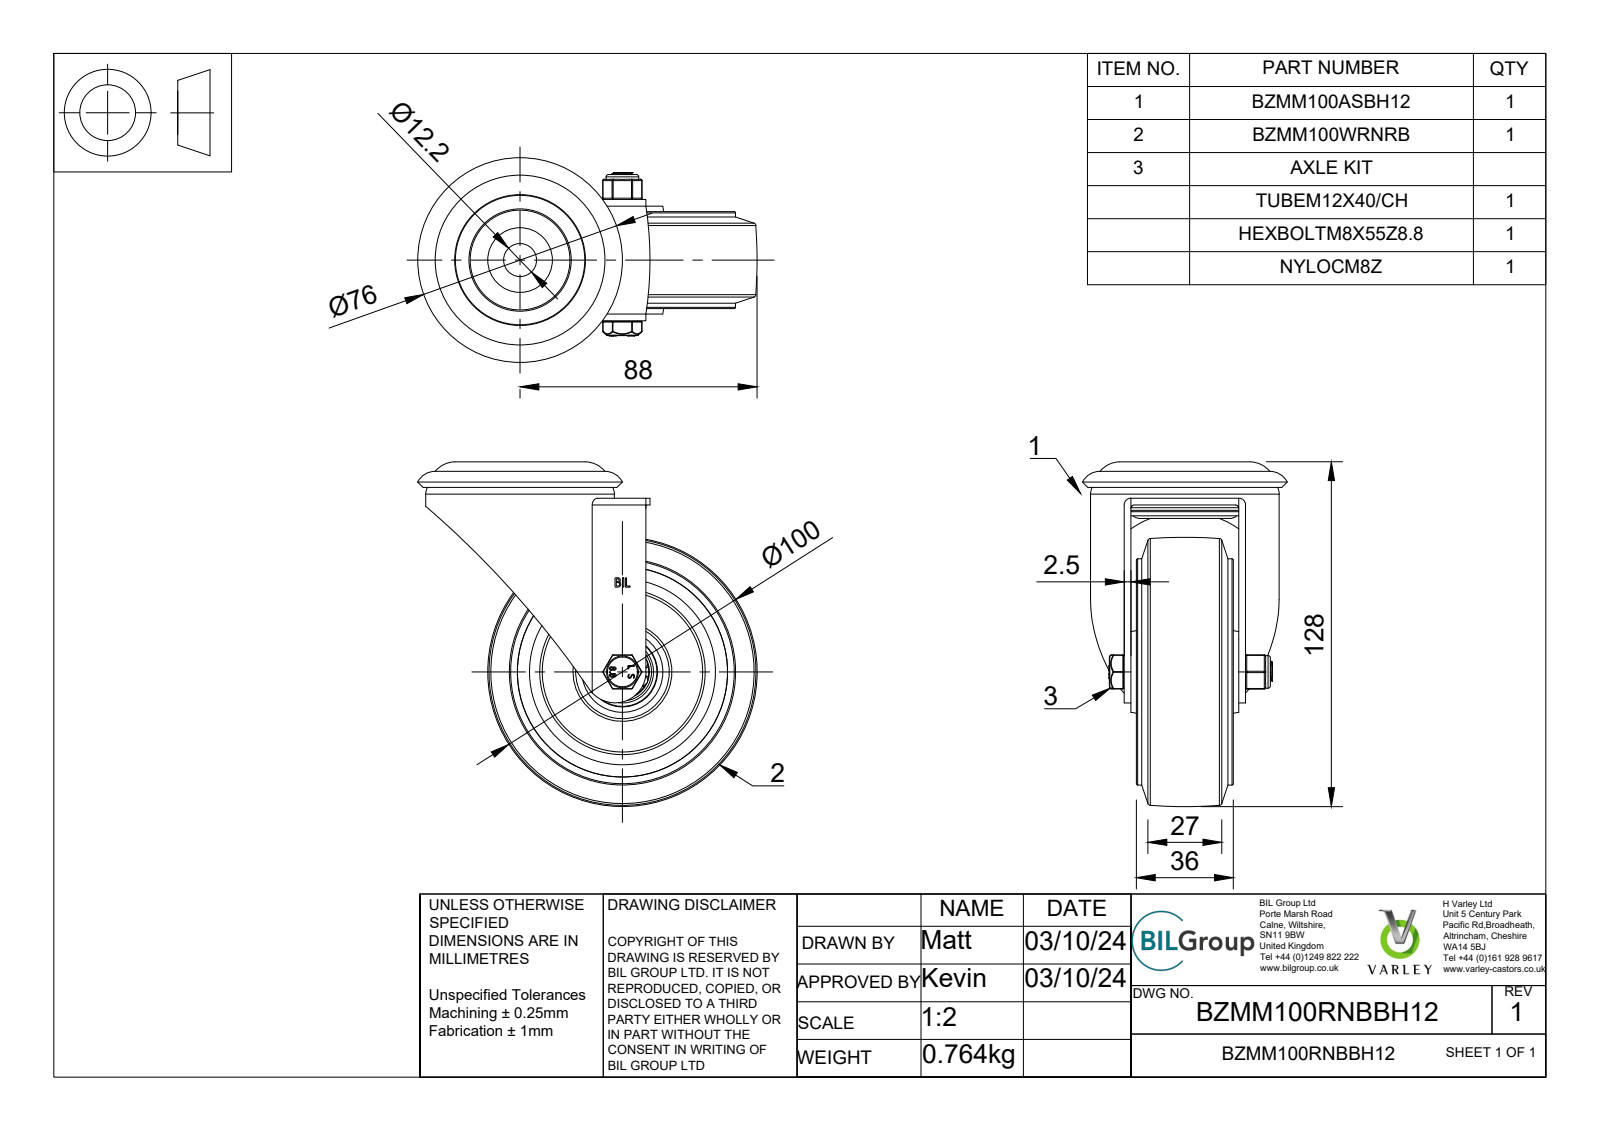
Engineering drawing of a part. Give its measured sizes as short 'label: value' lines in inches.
name: BZMM100RNBBH12 v3; BZMM100ASBH12 v1; ZINC PLATED PRESSED STEEL HEAD; ZINC PLATED, PRESSED STEEL FORKS (+7 more)
written by: Autodesk Translation Framework v13.20.0.188 (AUTOMOTIVE_DESIGN)
unit: in
bodies: 17 solids, 440 faces (177 planar, 153 cylindrical, 110 other)
size: 5.039 × 4.961 × 2.992
volume: 15.76 in³; area: 168.2 in²
holes: 2× ⌀0.026, 1× ⌀0.315, 1× ⌀0.323, 1× ⌀0.331, 1× ⌀0.339, 1× ⌀0.48, 1× ⌀0.492, 1× ⌀0.787, 1× ⌀1.024, 1× ⌀2.559, 1× ⌀2.835, 1× ⌀3.071
bosses: 8× ⌀0.148, 1× ⌀3.307, 1× ⌀2.756, 1× ⌀1.949, 1× ⌀1.496, 1× ⌀0.945, 1× ⌀0.839, 1× ⌀0.768
rounds: 18× R0.02, 12× R0.01, 4× R0.013, 4× R0.025, 4× R0.049, 2× R0.025, 2× R0.025, 2× R0.098
face distances: 0.098, 0.079, 0.906, 0.591, 0.984, 1.496, 0.512, 0.177, 1.083, 0.689
hole spacings: 0.127, 0.098
